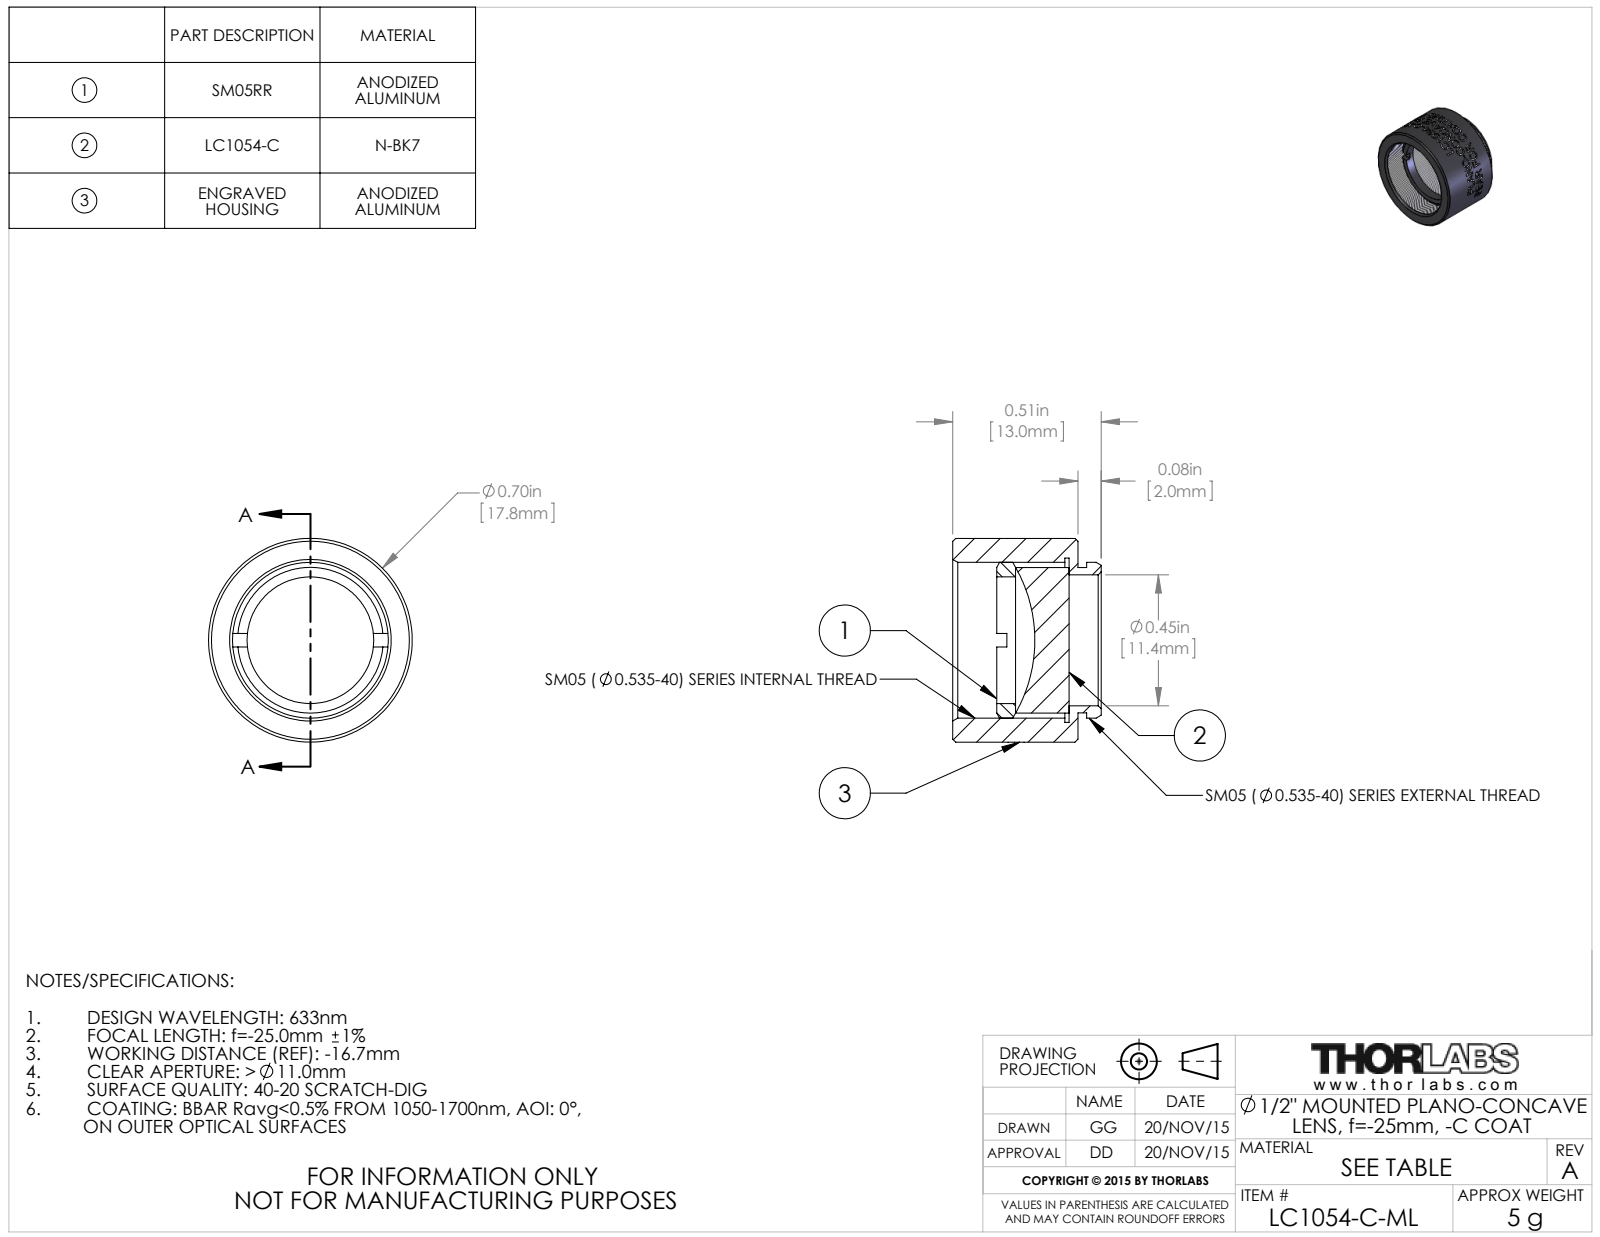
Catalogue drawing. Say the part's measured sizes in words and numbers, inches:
The part is named "TTN045242-E0W". Its 3-D file was written by "SolidWorks 2014 (CONFIG_CONTROL_DESIGN)". It is 3 solids with 149 faces: 16 planar, 116 cylindrical and 17 other. Overall it measures 0.7 by 0.7 by 0.51 inches. Its volume is 0.108 cubic inches and its surface area 3.431 square inches. Round holes: 1 of diameter 0.435, 1 of diameter 0.45, 1 of diameter 0.535, 1 of diameter 0.565. Round bosses or shafts: 1 of diameter 0.7, 1 of diameter 0.535, 1 of diameter 0.5, 1 of diameter 0.499. The main face-to-face distances are 0.03, 0.43, 0.4, 0.214, 0.184, 0.216, 0.28, 0.249, 0.065, 0.151.
